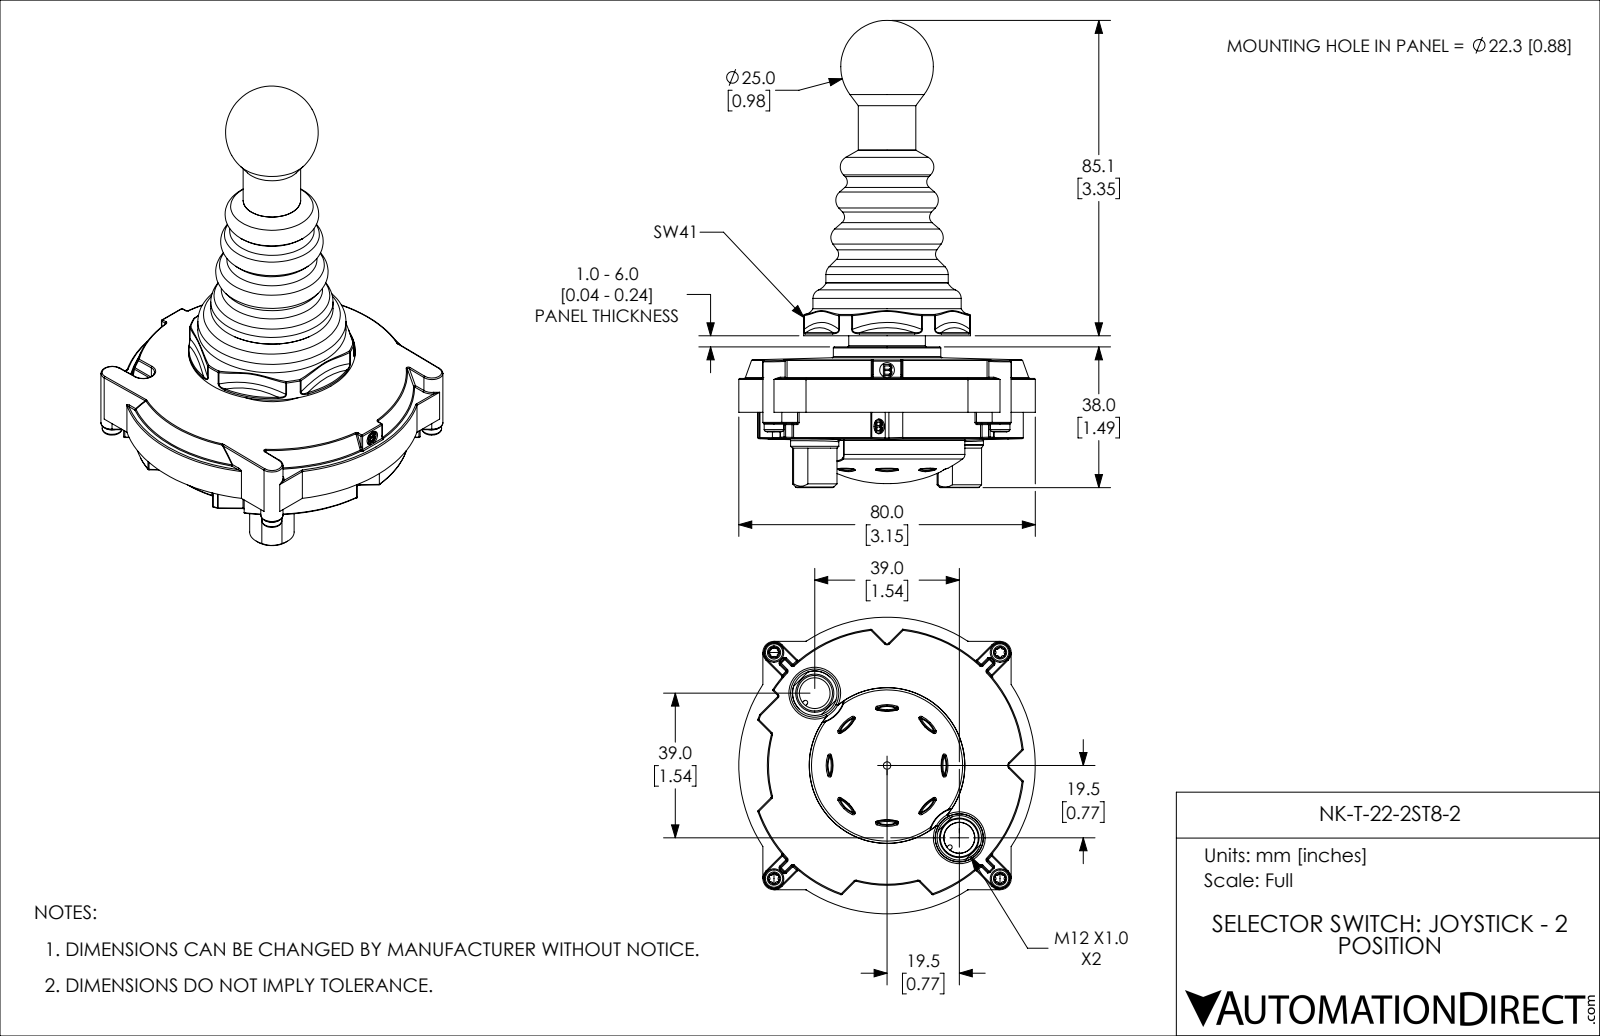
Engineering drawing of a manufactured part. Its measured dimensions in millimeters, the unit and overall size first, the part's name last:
Units: millimetres
Overall size (bounding box): 126.01 × 80 × 80
Round holes (diameter × count): ⌀4 ×5, ⌀2.93 ×4, ⌀8.3 ×2, ⌀8.4 ×1, ⌀31.2 ×1, ⌀37.1 ×1, ⌀40.1 ×1
Round bosses / shafts (diameter × count): ⌀5.3 ×4, ⌀13 ×2, ⌀45 ×1, ⌀42 ×1, ⌀40 ×1, ⌀33.1 ×1, ⌀33 ×1, ⌀29 ×1
Partial cylindrical surfaces — rounded edges, fillets, slot ends (radius × count): R0.3 ×115, R0.19 ×44, R0.5 ×12, R0.6 ×8, R2.58 ×8, R9 ×8, R3 ×5, R0.69 ×2
Main face-to-face distances: 34.95, 14.1, 20.85, 67, 70.71, 49.86, 35.76, 25.8, 17.3, 9.15
Hole centre spacings: 61, 43.13, 4.5, 51.2, 51.21, 56.5, 86.27, 15.53
Volume: 166 503 mm³ · Surface area: 33 117 mm²
Bodies: 4 solids, 1383 faces (383 planar, 350 cylindrical, 650 other)
Part name (STEP PRODUCT): NK-T-22-2ST8-2
STEP written by: SolidWorks 2019 (CONFIG_CONTROL_DESIGN)
